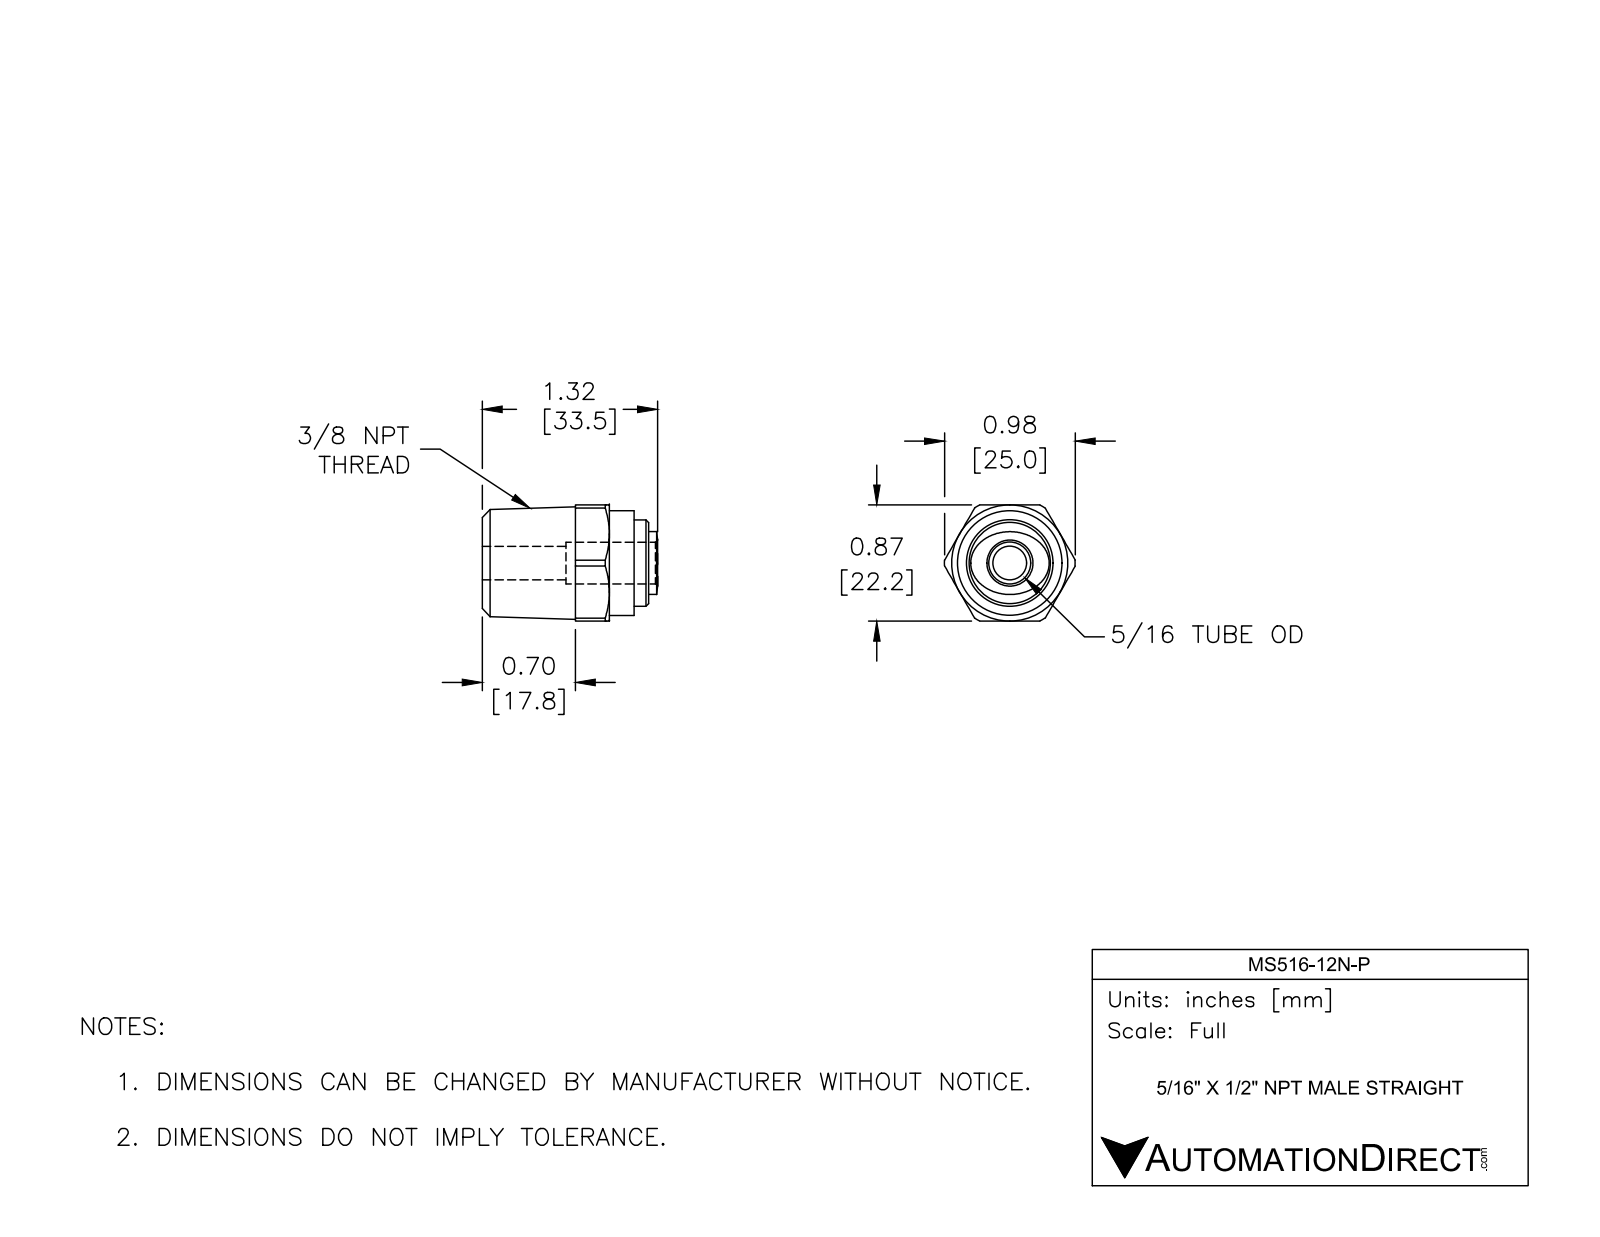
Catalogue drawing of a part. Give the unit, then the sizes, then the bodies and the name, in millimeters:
Units: millimetres
Overall size (bounding box): 33.5 × 25 × 22.2
Round holes (diameter × count): ⌀6.4 ×1, ⌀8 ×1
Round bosses / shafts (diameter × count): ⌀20 ×1, ⌀16.5 ×1
Partial cylindrical surfaces — rounded edges, fillets, slot ends (radius × count): R12.5 ×1
Main face-to-face distances: 22.2, 29, 24.3, 4.7, 17.8, 6.5, 11.2, 31.8, 14, 7.5
Volume: 9 730 mm³ · Surface area: 3 587 mm²
Bodies: 1 solid, 44 faces (12 planar, 14 cylindrical, 18 other)
Part name (STEP PRODUCT): MS516-12N-P
STEP written by: SolidWorks 2017 (AUTOMOTIVE_DESIGN)
